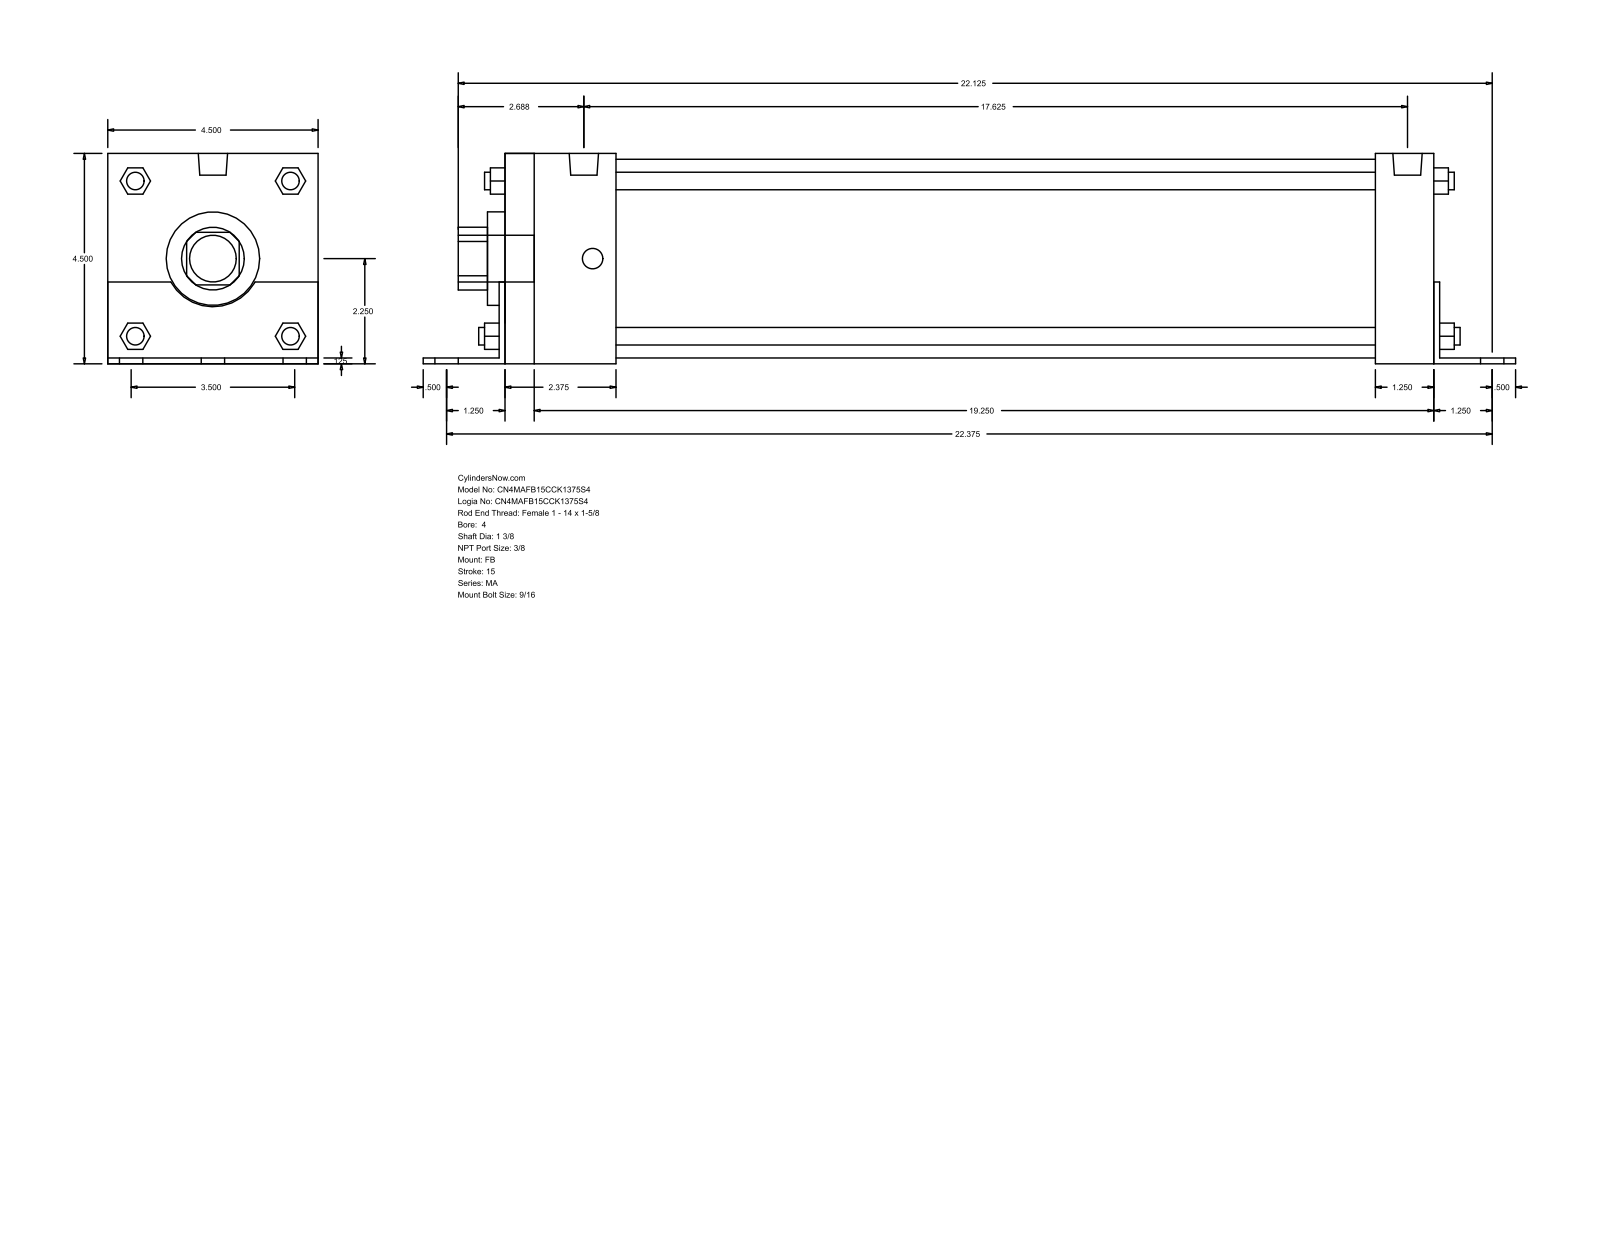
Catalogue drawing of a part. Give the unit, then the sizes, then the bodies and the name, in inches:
Units: inches
Overall size (bounding box): 23.375 × 4.502 × 4.5
Round holes (diameter × count): ⌀1.375 ×1, ⌀2 ×1, ⌀4.25 ×1
Round bosses / shafts (diameter × count): ⌀0.563 ×6, ⌀0.437 ×4, ⌀0.375 ×4, ⌀0.627 ×2, ⌀1 ×1
Partial cylindrical surfaces — rounded edges, fillets, slot ends (radius × count): R0.672 ×1, R1.03 ×1
Main face-to-face distances: 4.5, 0.125, 4.502, 0.123, 4.377, 20, 19.875, 2.375, 20.125, 1.25
Bodies: 0 solids, 140 faces (105 planar, 35 cylindrical, 0 other)
Part name (STEP PRODUCT): MA_FB__0400_1.375
STEP written by: GSSL Pune (CONFIG_CONTROL_DESIGN)
